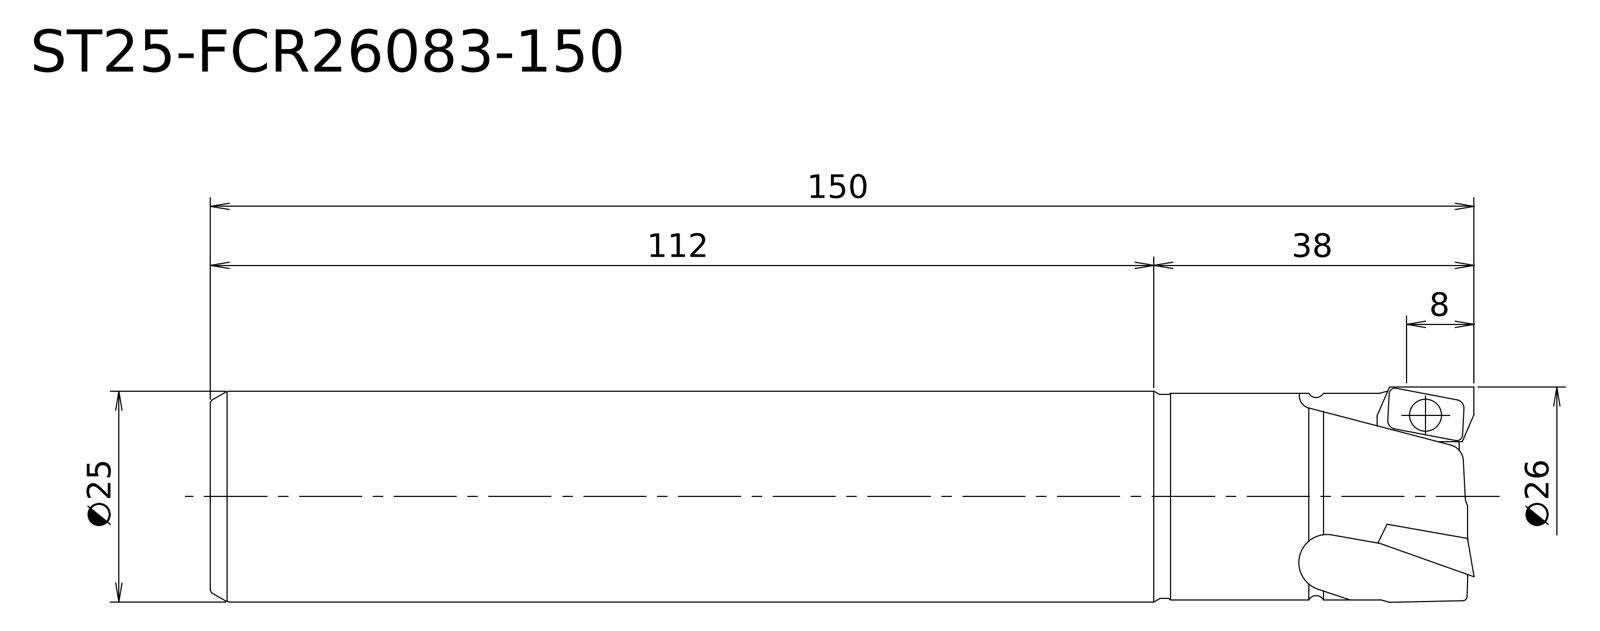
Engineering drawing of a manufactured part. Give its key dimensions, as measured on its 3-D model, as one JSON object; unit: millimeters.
{"step_written_by": "Kubotek KeyCreator V8.5.1 (14335) (CONFIG_CONTROL_DESIGN)", "units": "millimeters", "bodies": {"solids": 1, "faces": 7, "planar": 2, "cylindrical": 3, "other": 2}, "overall_size": [150, 26, 26], "volume_mm3": 73503, "surface_area_mm2": 12836, "round_bosses_or_shafts": [[26, 1], [25, 1], [24.5, 1]], "face_to_face_distances": [150]}
